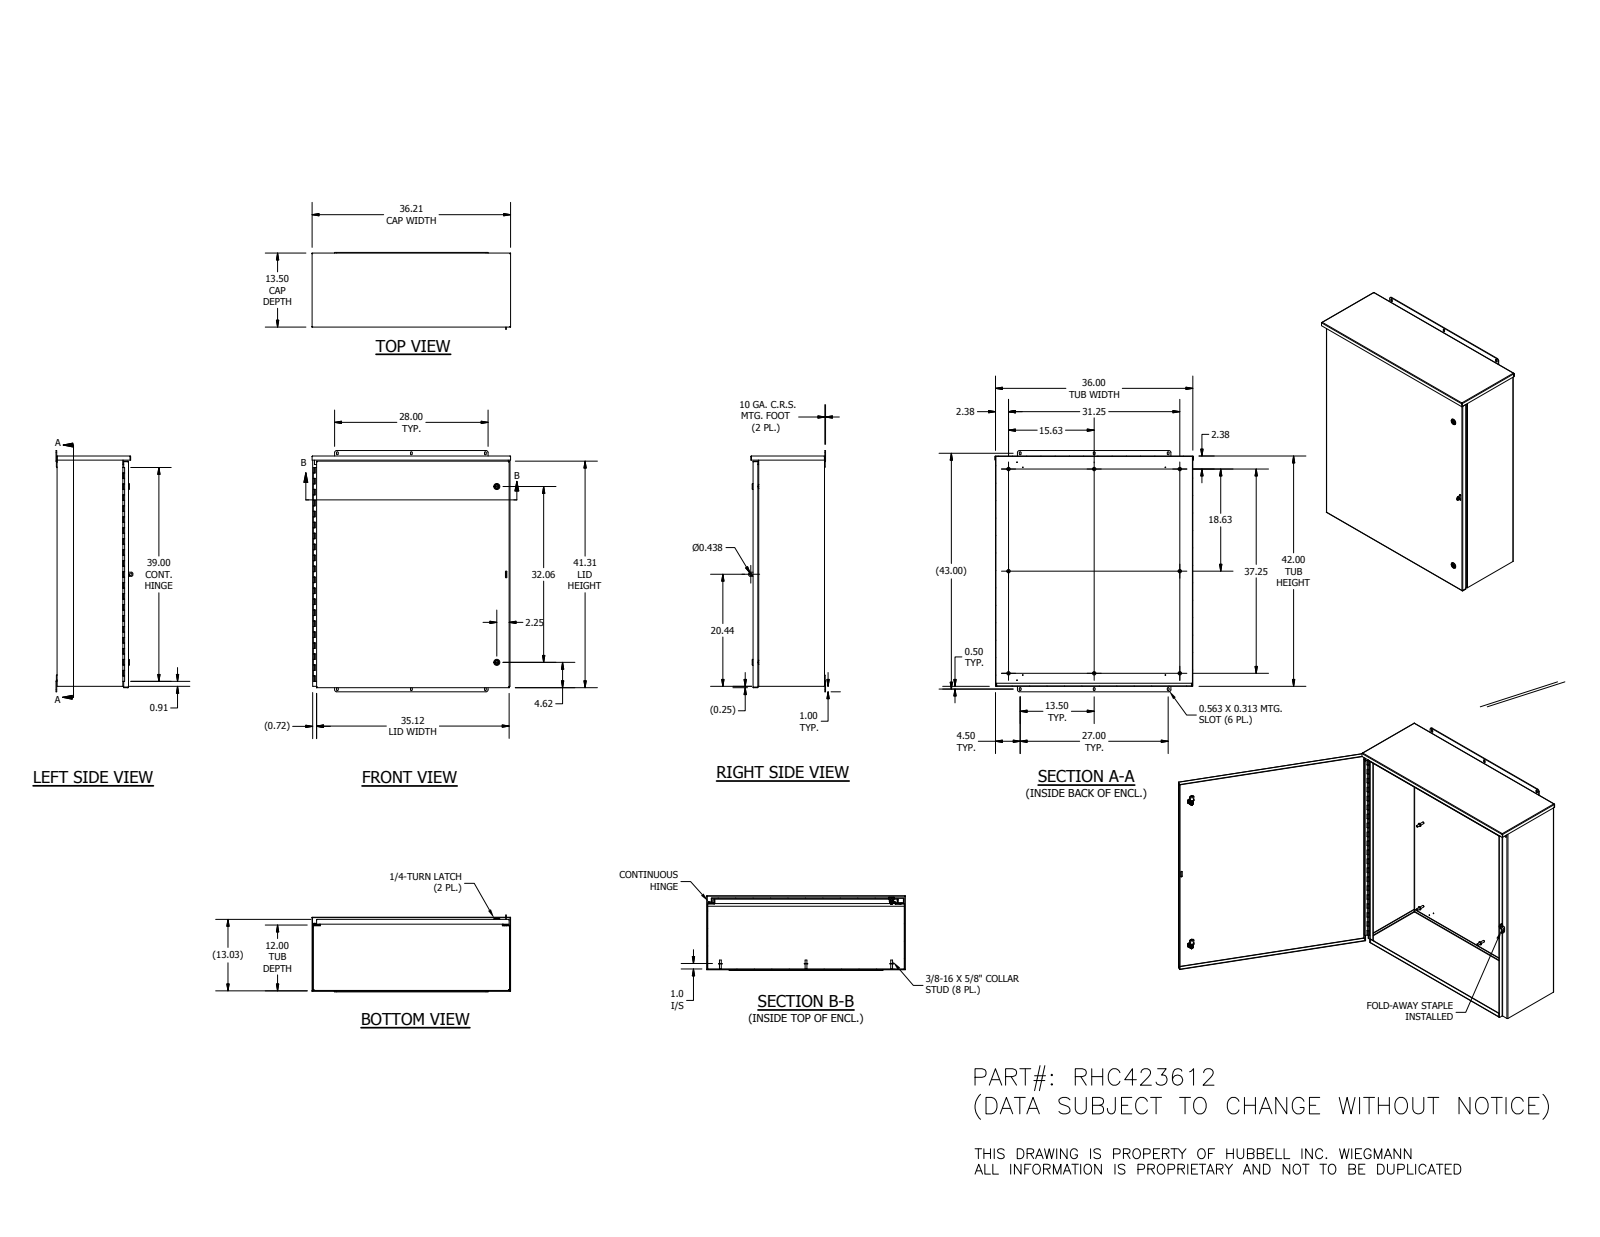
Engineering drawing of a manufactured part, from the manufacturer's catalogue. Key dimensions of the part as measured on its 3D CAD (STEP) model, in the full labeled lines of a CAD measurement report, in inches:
Part name (STEP PRODUCT): RHC423612BLR; RHC36TOP; RHC3612BTM; RHC4236LID (+8 more)
STEP written by: Autodesk Inventor 2016 (AUTOMOTIVE_DESIGN)
Units: inches
Bodies: 34 solids, 1556 faces (899 planar, 503 cylindrical, 154 other)
Overall size (bounding box): 44 × 36.211 × 14.012
Volume: 429.6 in³ · Surface area: 11 470 in²
Round holes (diameter × count): ⌀0.12 ×6, ⌀0.125 ×2, ⌀0.197 ×2, ⌀0.315 ×2, ⌀0.394 ×2, ⌀0.402 ×2, ⌀0.634 ×2, ⌀0.802 ×2, ⌀0.198 ×1, ⌀0.201 ×1, ⌀0.437 ×1
Round bosses / shafts (diameter × count): ⌀0.625 ×8, ⌀0.33 ×8, ⌀1.102 ×2, ⌀1.063 ×2, ⌀0.906 ×2, ⌀0.78 ×2, ⌀0.622 ×2, ⌀0.598 ×2
Partial cylindrical surfaces — rounded edges, fillets, slot ends (radius × count): R0.012 ×56, R0.02 ×21, R0.137 ×13, R0.156 ×12, R0.063 ×10, R0.125 ×10, R0.031 ×8, R0.105 ×8
Main face-to-face distances: 0.074, 12.959, 13.033, 12.885, 35.926, 41.926, 35.852, 36, 41.852, 42
Hole centre spacings: 1.414, 26, 27.076, 37.88, 38.83, 45.944, 47.317, 0.354
